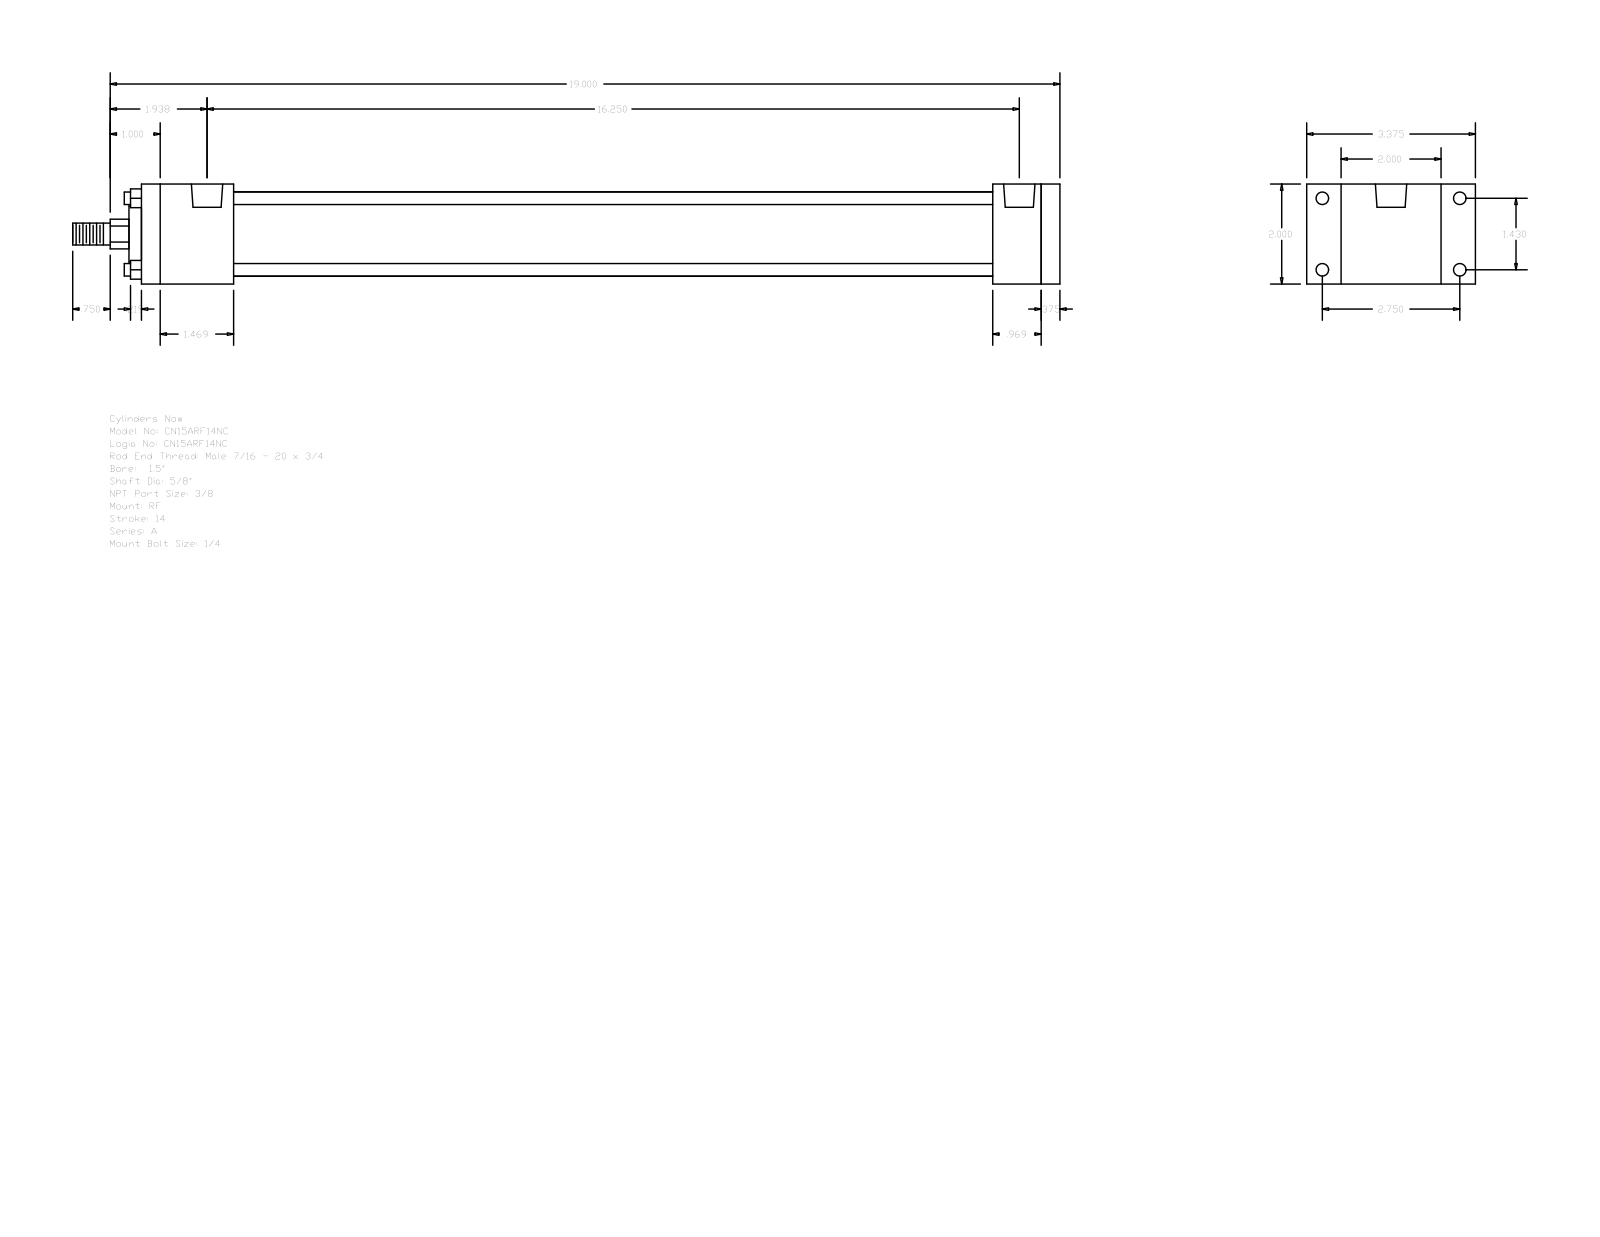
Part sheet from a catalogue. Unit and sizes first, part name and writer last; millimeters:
Units: millimetres
Overall size (bounding box): 501.65 × 85.72 × 50.8
Round holes (diameter × count): ⌀5.56 ×4, ⌀6.35 ×4, ⌀15.93 ×2
Round bosses / shafts (diameter × count): ⌀6.35 ×4, ⌀42.93 ×1, ⌀28.57 ×1, ⌀15.88 ×1, ⌀11.11 ×1
Partial cylindrical surfaces — rounded edges, fillets, slot ends (radius × count): R7.54 ×1
Main face-to-face distances: 50.8, 9.53, 466.72, 457.19, 432.59, 24.6, 34.13, 46.83, 385.76, 410.36
Hole centre spacings: 3.97, 36.32, 69.84, 78.72, 404.81, 408.78, 412.75
Bodies: 0 solids, 92 faces (64 planar, 28 cylindrical, 0 other)
Part name (STEP PRODUCT): A_RF__0150_0.625
STEP written by: GSSL Pune (CONFIG_CONTROL_DESIGN)
